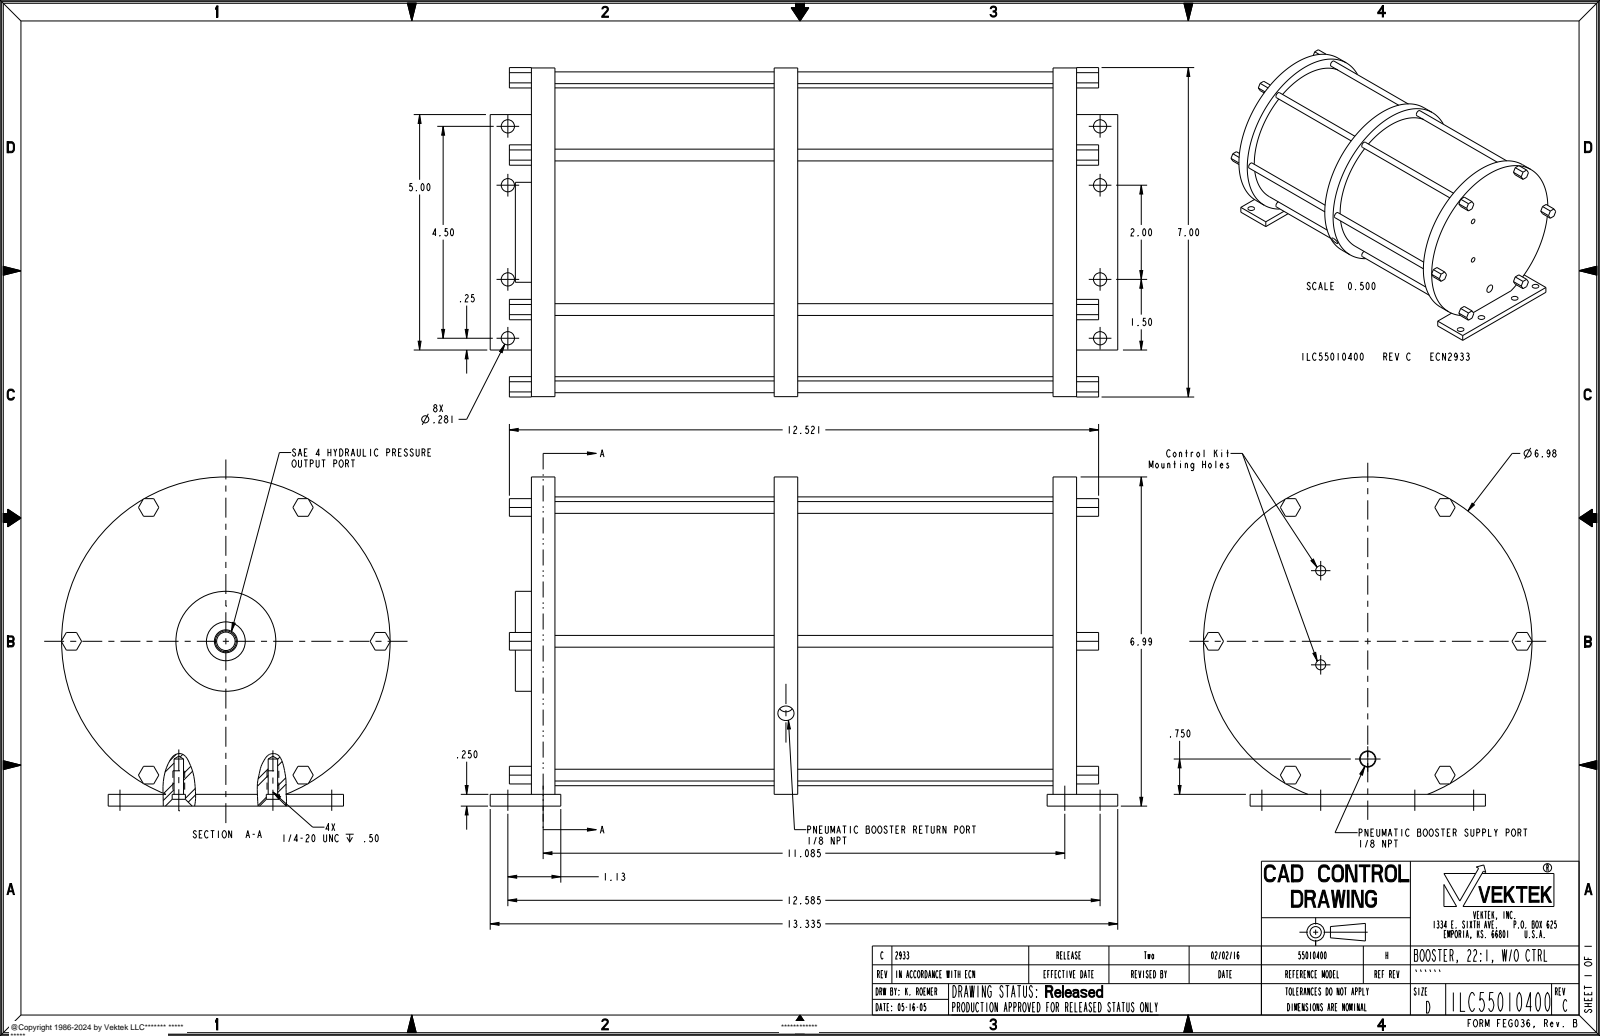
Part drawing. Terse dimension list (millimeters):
name: ILC55010400
written by: PRO/ENGINEER BY PARAMETRIC TECHNOLOGY CORPORATION, 2013320 (CONFIG_CONTROL_DESIGN)
unit: mm
bodies: 1 solid, 245 faces (128 planar, 87 cylindrical, 30 other)
size: 338.7 × 177.7 × 177.5
volume: 5 945 000 mm³; area: 278 600 mm²
holes: 12× ⌀7.1, 6× ⌀6.4, 4× ⌀5.1, 2× ⌀5.4, 1× ⌀10, 1× ⌀21
bosses: 6× ⌀6.4, 1× ⌀177.3, 1× ⌀155.8, 1× ⌀53.9, 1× ⌀11.1
face distances: 294.3, 12.7, 281.6, 131, 150.5, 6.4, 143.7, 118.3, 268.9, 163.2
hole spacings: 50.8, 19.1, 31.8, 37, 54.3, 82.6, 84.7, 300.6
